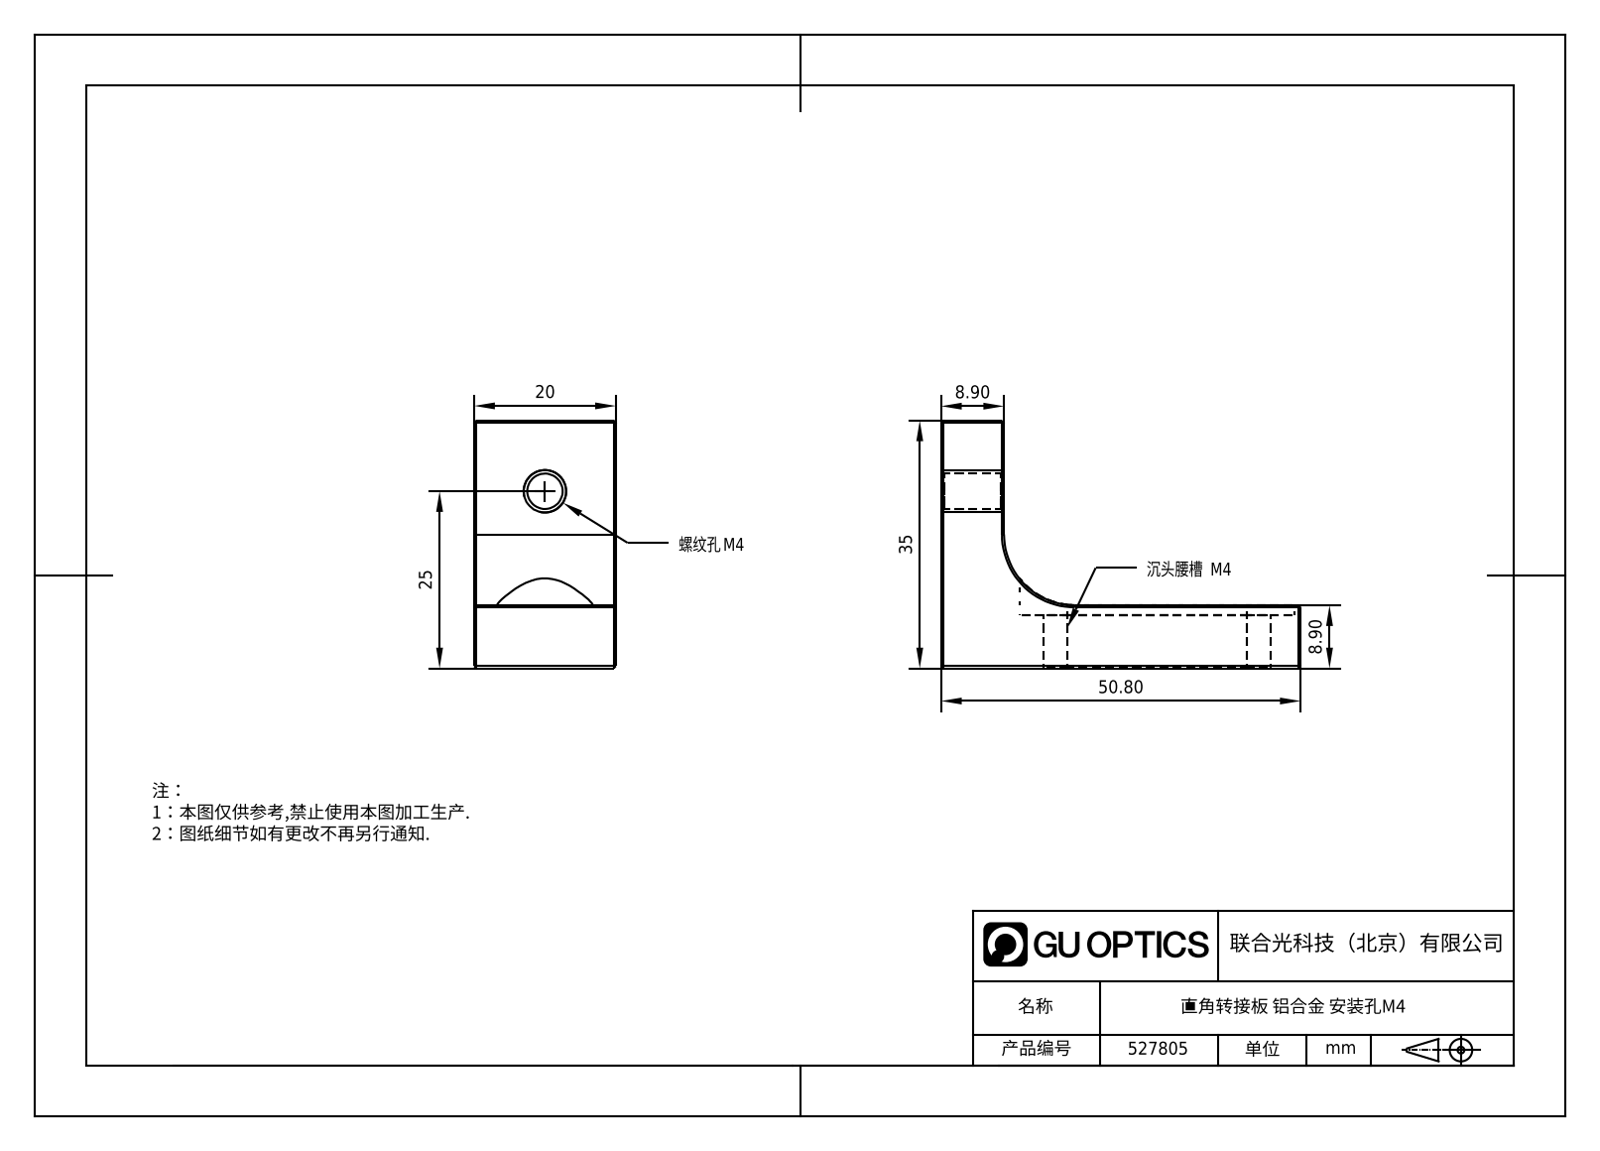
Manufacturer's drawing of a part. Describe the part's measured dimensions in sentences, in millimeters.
The part is named "7.5.4.9-MCS-50B1". Its 3-D file was written by "SolidWorks 2021 (CONFIG_CONTROL_DESIGN)". It is 1 solid with 55 faces: 40 planar, 9 cylindrical and 6 other. Overall it measures 50.8 by 35 by 20 millimeters. Its volume is 12 493 cubic millimeters and its surface area 5 108 square millimeters. Round holes: 1 of diameter 3.3. Partial cylindrical surfaces (rounded edges, fillets, slot ends): 2 of radius 2.3, 2 of radius 5.25, 1 of radius 10. The main face-to-face distances are 20, 8.9, 7.7, 12.3, 7.5, 1.4, 4.6, 35, 27.5, 26.1.
